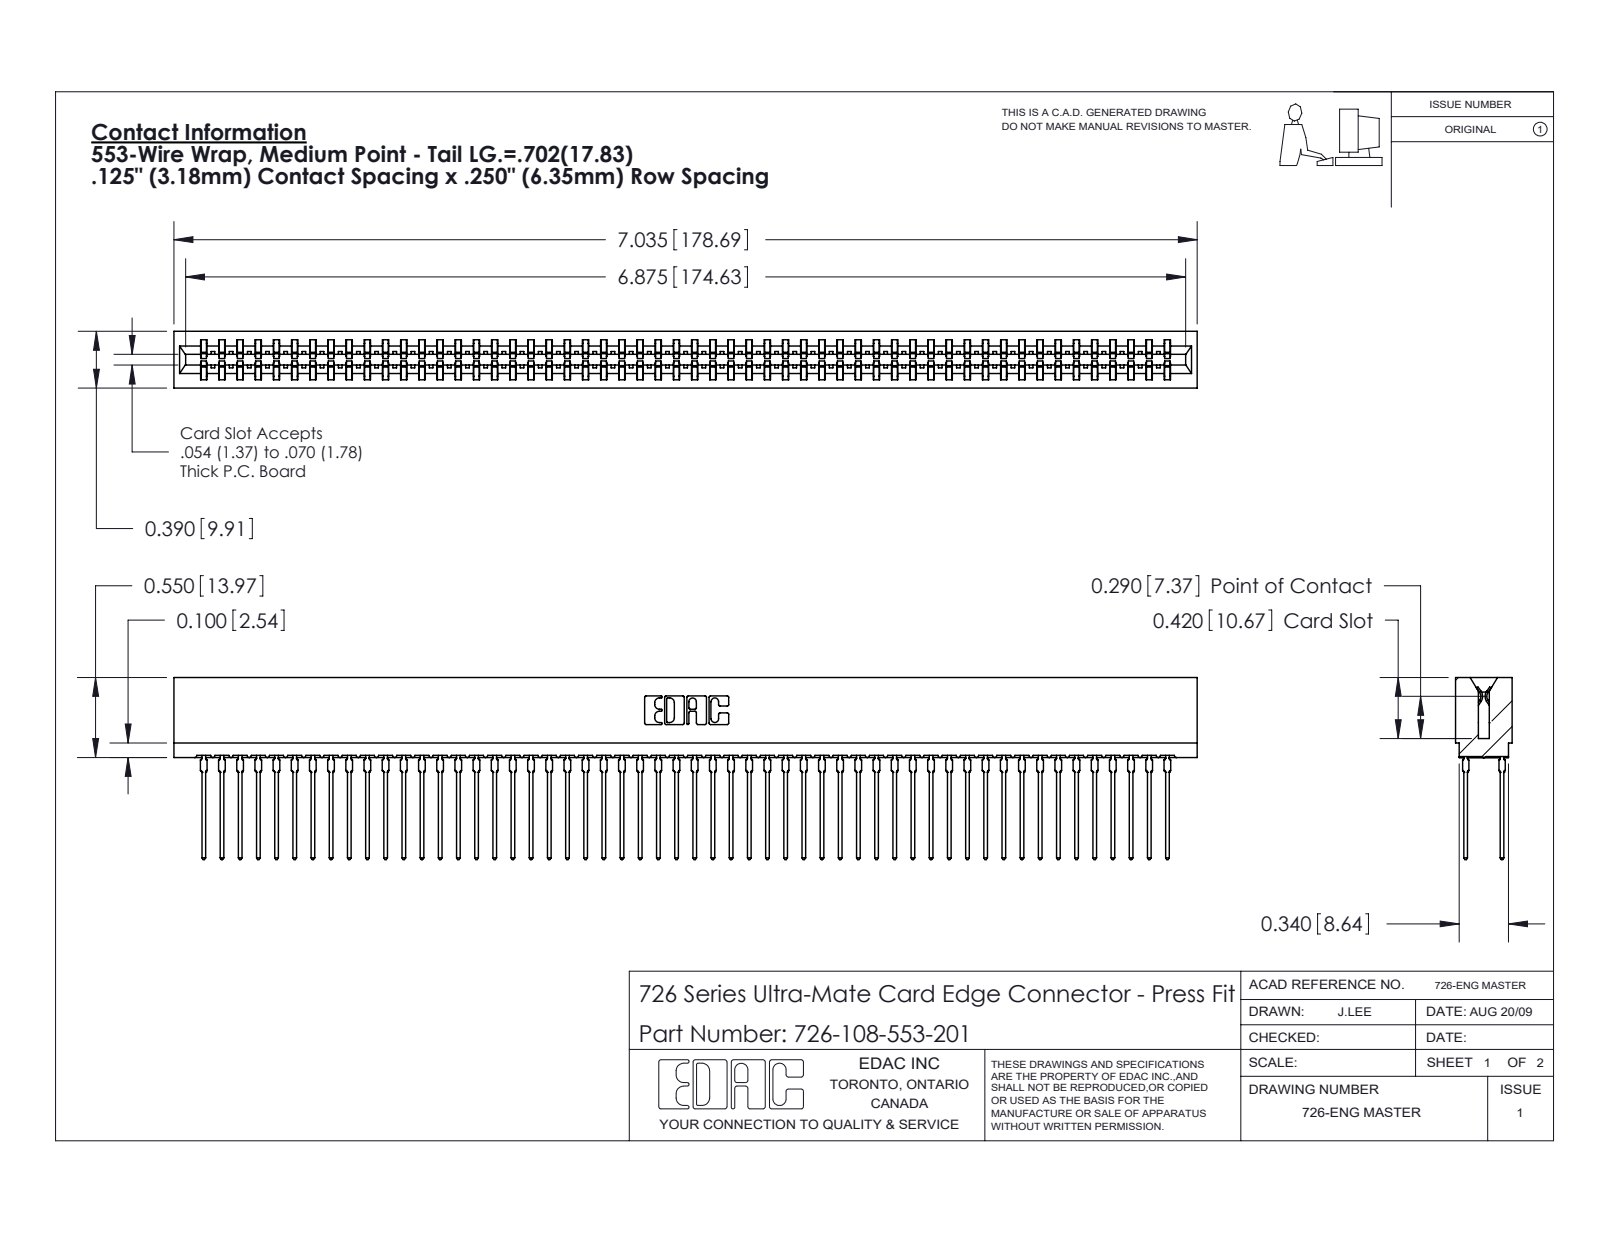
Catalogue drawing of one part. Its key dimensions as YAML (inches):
part_name: "726 Part_.515 Slot Depth - 01; 746-292-001_553; 726-108-553-201"
step_written_by: "SolidWorks 2020 (CONFIG_CONTROL_DESIGN)"
units: inches
bodies: {solids: 109, faces: 9763, planar: 5023, cylindrical: 1932, other: 2808}
overall_size: [7.035, 1.251, 0.39]
volume: 1.029
surface_area: 47.28
partial_cylinders:
  - {radius: 0.021, count: 216}
  - {radius: 0.015, count: 55}
  - {radius: 0.01, count: 22}
  - {radius: 0.005, count: 8}
  - {radius: 0.011, count: 8}
  - {radius: 0.007, count: 6}
  - {radius: 0.031, count: 6}
  - {radius: 0.026, count: 3}
face_to_face_distances: [0.057, 0.333, 0.025, 0.307, 0.25, 0.39, 0.083, 0.275, 0.225, 0.365]
